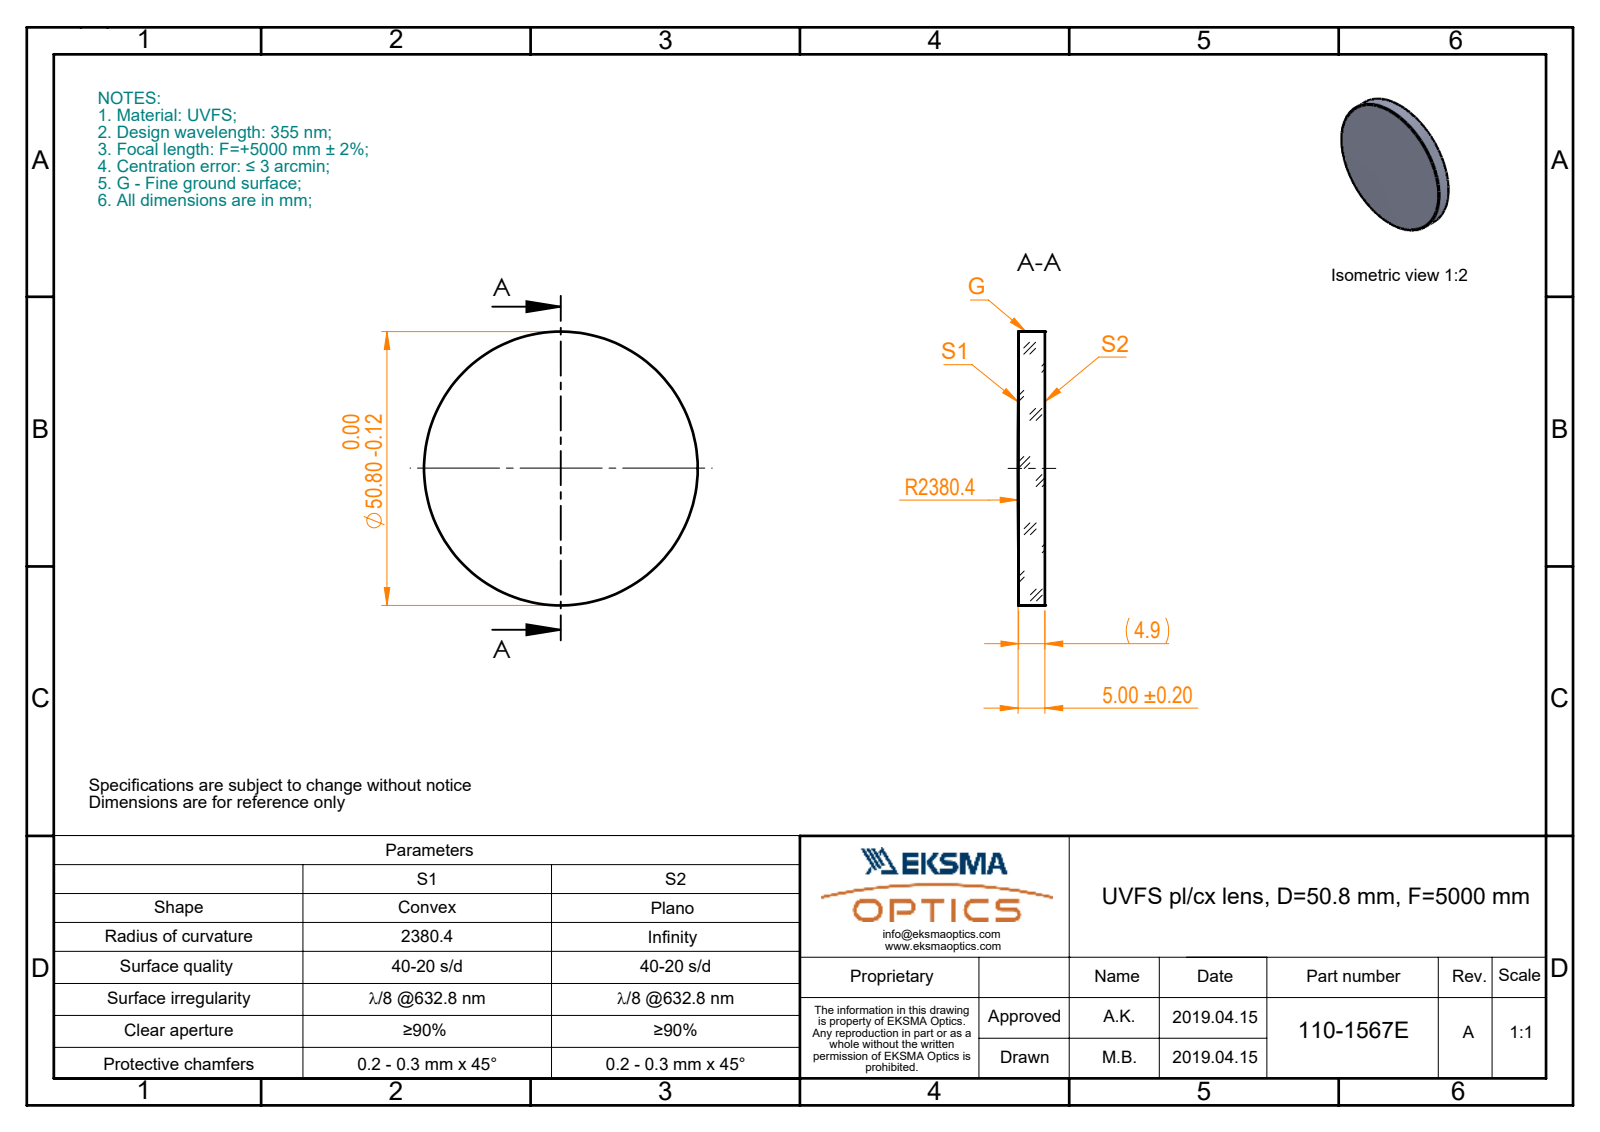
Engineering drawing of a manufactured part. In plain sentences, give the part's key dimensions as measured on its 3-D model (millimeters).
The part is named "110-1567E UVFS pl-cx 50.8 F5000". Its 3-D file was written by "SolidWorks 2017 (CONFIG_CONTROL_DESIGN)". It is 1 solid with 5 faces: 1 planar, 2 cylindrical and 2 other. Overall it measures 50.8 by 50.8 by 5 millimeters. Its volume is 9 997 cubic millimeters and its surface area 4 830 square millimeters. Round bosses or shafts: 1 of diameter 50.8.
